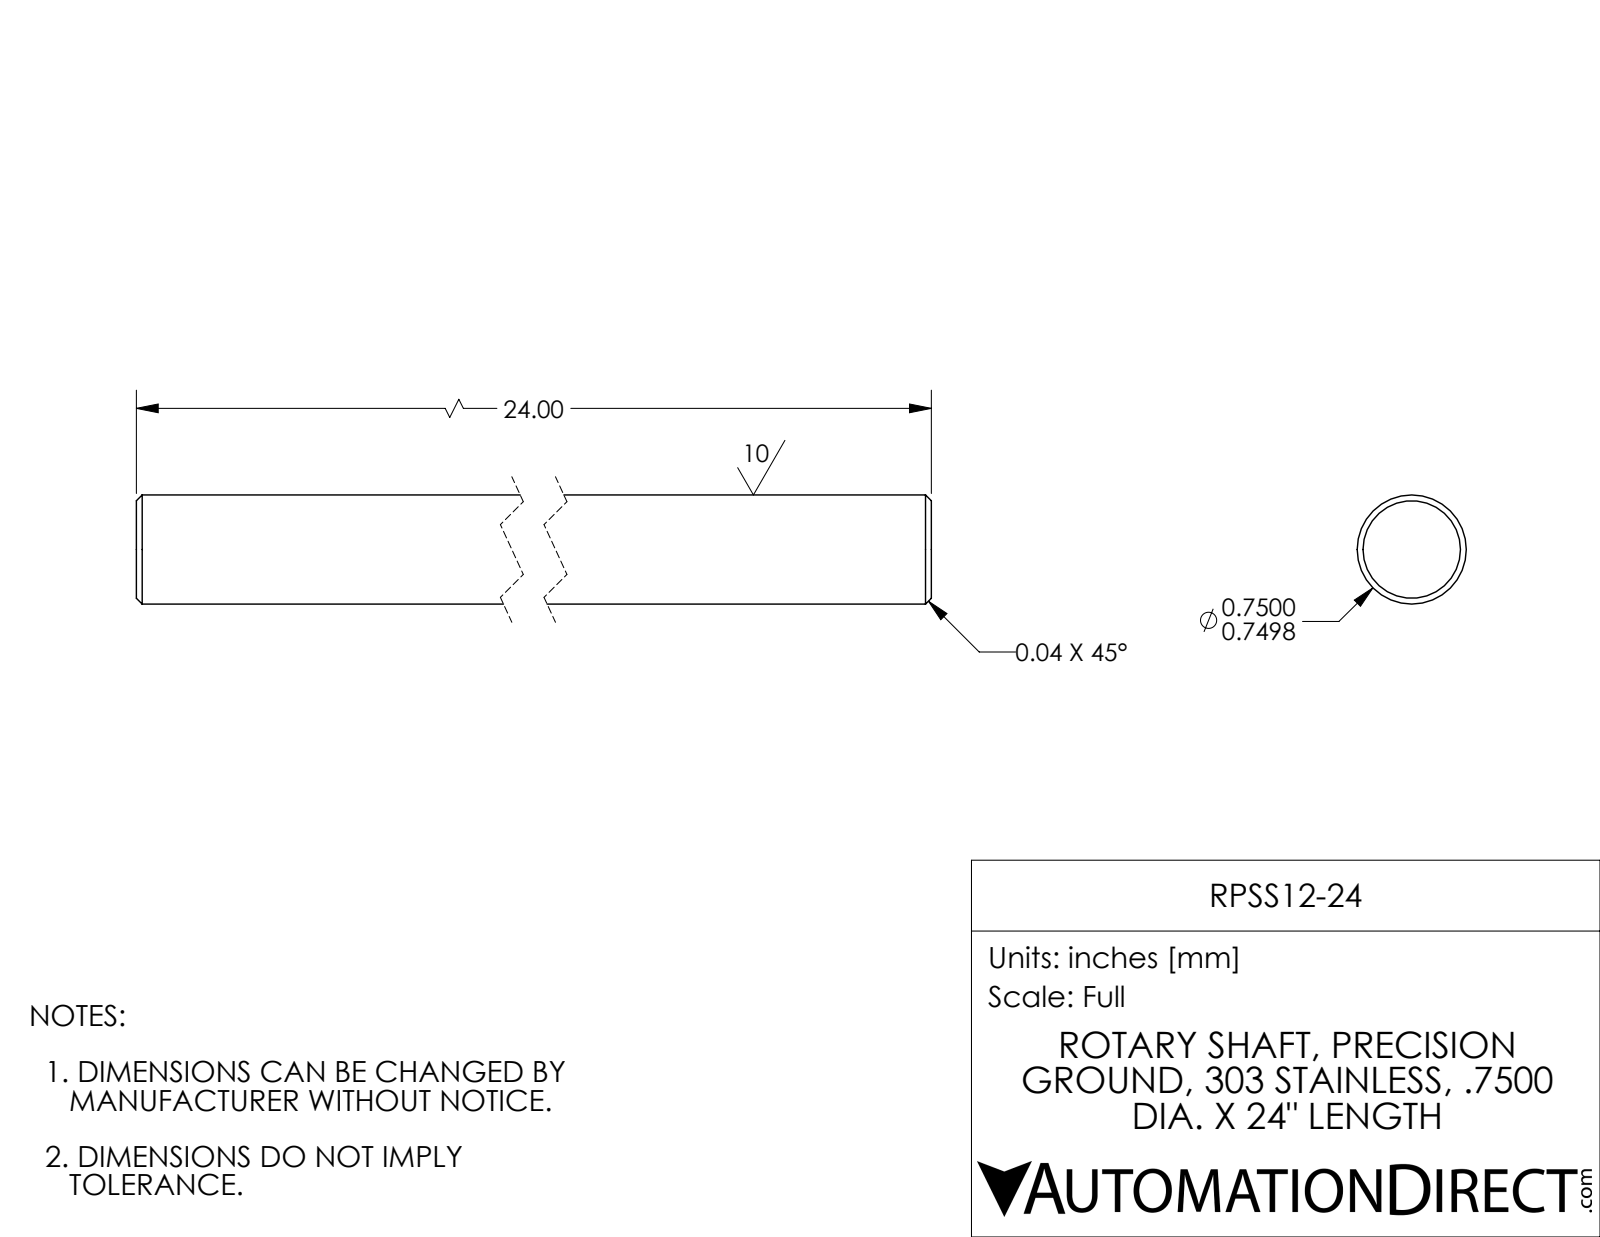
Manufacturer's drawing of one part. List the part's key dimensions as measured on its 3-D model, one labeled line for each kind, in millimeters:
Part name (STEP PRODUCT): RPSS12-24
STEP written by: SolidWorks 2017 (AUTOMOTIVE_DESIGN)
Units: millimetres
Bodies: 1 solid, 8 faces (2 planar, 2 cylindrical, 4 other)
Overall size (bounding box): 609.6 × 19.1 × 19.1
Volume: 173 700 mm³ · Surface area: 36 980 mm²
Round bosses / shafts (diameter × count): ⌀19.1 ×1
Main face-to-face distances: 609.6
